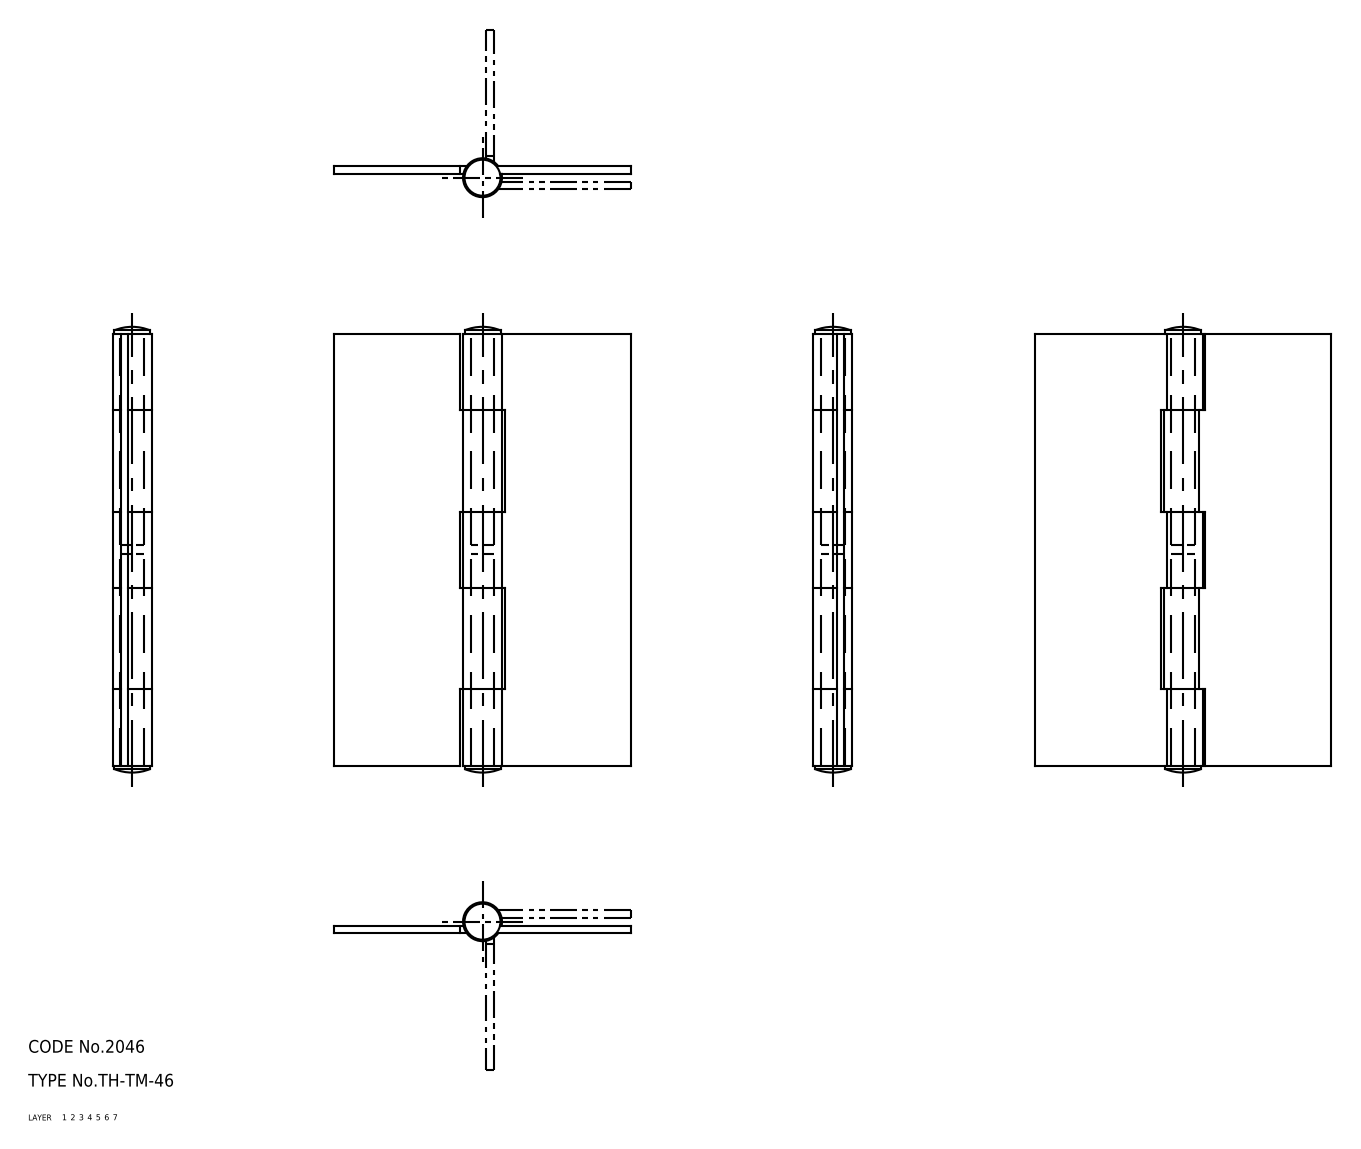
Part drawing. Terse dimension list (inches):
name: 67111588; 67111601; 67111614; 67111627
written by: CADfix (AUTOMOTIVE_DESIGN)
unit: in
bodies: 4 solids, 52 faces (0 planar, 0 cylindrical, 52 other)
size: 4.146 × 2.756 × 0.362
volume: 1.096 in³; area: 31.75 in²
